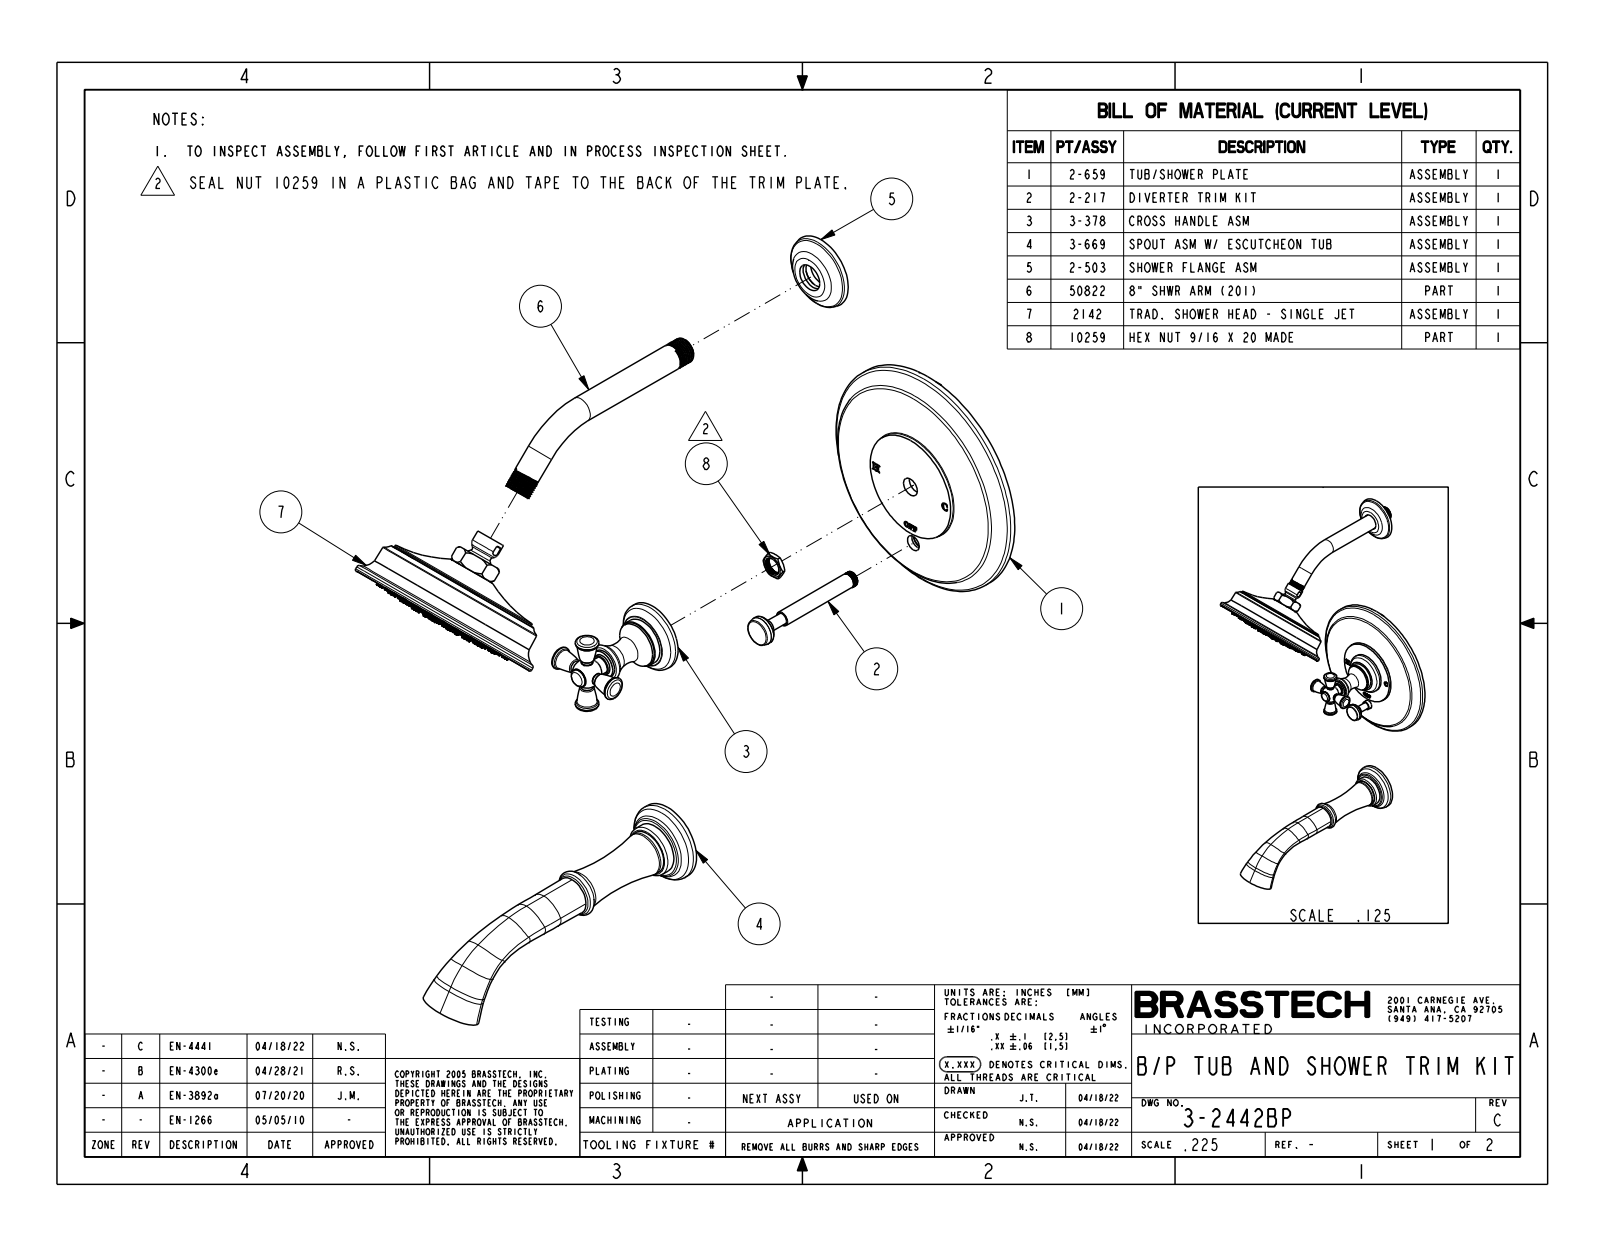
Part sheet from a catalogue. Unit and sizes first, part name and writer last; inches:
Units: inches
Overall size (bounding box): 20.973 × 10.691 × 7.5
Round holes (diameter × count): ⌀0.05 ×90, ⌀0.22 ×1, ⌀0.604 ×1, ⌀5.275 ×1
Round bosses / shafts (diameter × count): ⌀1.42 ×2, ⌀0.9 ×2, ⌀0.813 ×2, ⌀0.72 ×2, ⌀0.36 ×2, ⌀7.5 ×1, ⌀6.2 ×1, ⌀5.22 ×1
Main face-to-face distances: 0.625, 0.75, 0.125, 0.48, 0.145, 0.27, 1.014, 0.55, 0.07, 0.075
Hole centre spacings: 2.27, 0.48, 1.84, 0.952, 1.84, 1.408, 2.24, 2.602
Volume: 83.6 in³ · Surface area: 286.2 in²
Bodies: 3 solids, 1372 faces (280 planar, 258 cylindrical, 834 other)
Part name (STEP PRODUCT): 3-2442BP
STEP written by: CREO PARAMETRIC BY PTC INC, 2018400 (CONFIG_CONTROL_DESIGN)
